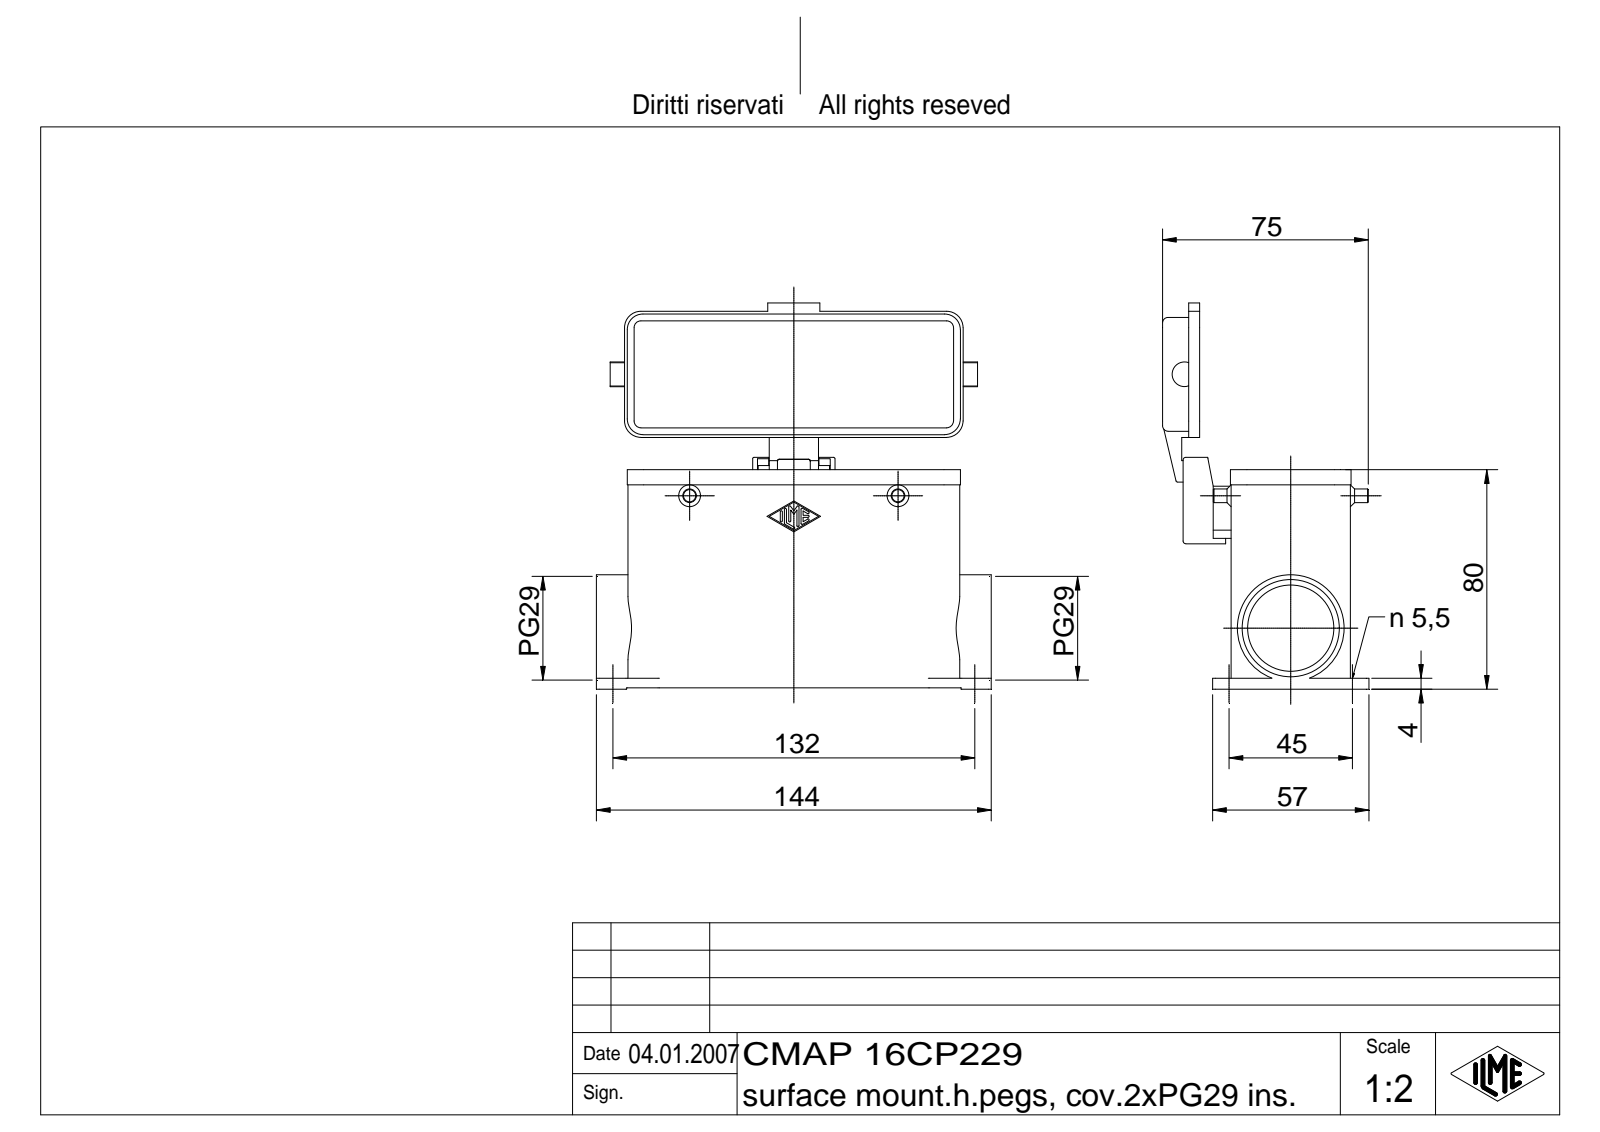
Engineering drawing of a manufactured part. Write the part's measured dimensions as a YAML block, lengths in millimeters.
part_name: "CMAP 16CP229"
step_written_by: "Autodesk Inventor 7 (AUTOMOTIVE_DESIGN)"
units: millimeters
bodies: {solids: 1, faces: 473, planar: 197, cylindrical: 166, other: 110}
overall_size: [144, 140.75, 75.25]
volume: 143301
surface_area: 91130
round_holes:
  - {diameter: 5.5, count: 4}
  - {diameter: 4, count: 1}
  - {diameter: 5, count: 1}
  - {diameter: 31.48, count: 1}
  - {diameter: 35.48, count: 1}
round_bosses_or_shafts:
  - {diameter: 5, count: 2}
  - {diameter: 3, count: 2}
  - {diameter: 38.98, count: 1}
  - {diameter: 7, count: 1}
  - {diameter: 4, count: 1}
partial_cylinders:
  - {radius: 0.38, count: 14}
  - {radius: 1, count: 14}
  - {radius: 6, count: 12}
  - {radius: 0.5, count: 10}
  - {radius: 0.7, count: 8}
  - {radius: 2, count: 8}
  - {radius: 2.5, count: 4}
  - {radius: 3, count: 4}
face_to_face_distances: [3, 40.5, 43.5, 37.5, 2.5, 3.5, 22.5, 63, 66, 25.5]
hole_center_spacings: [45, 132, 139.46]
